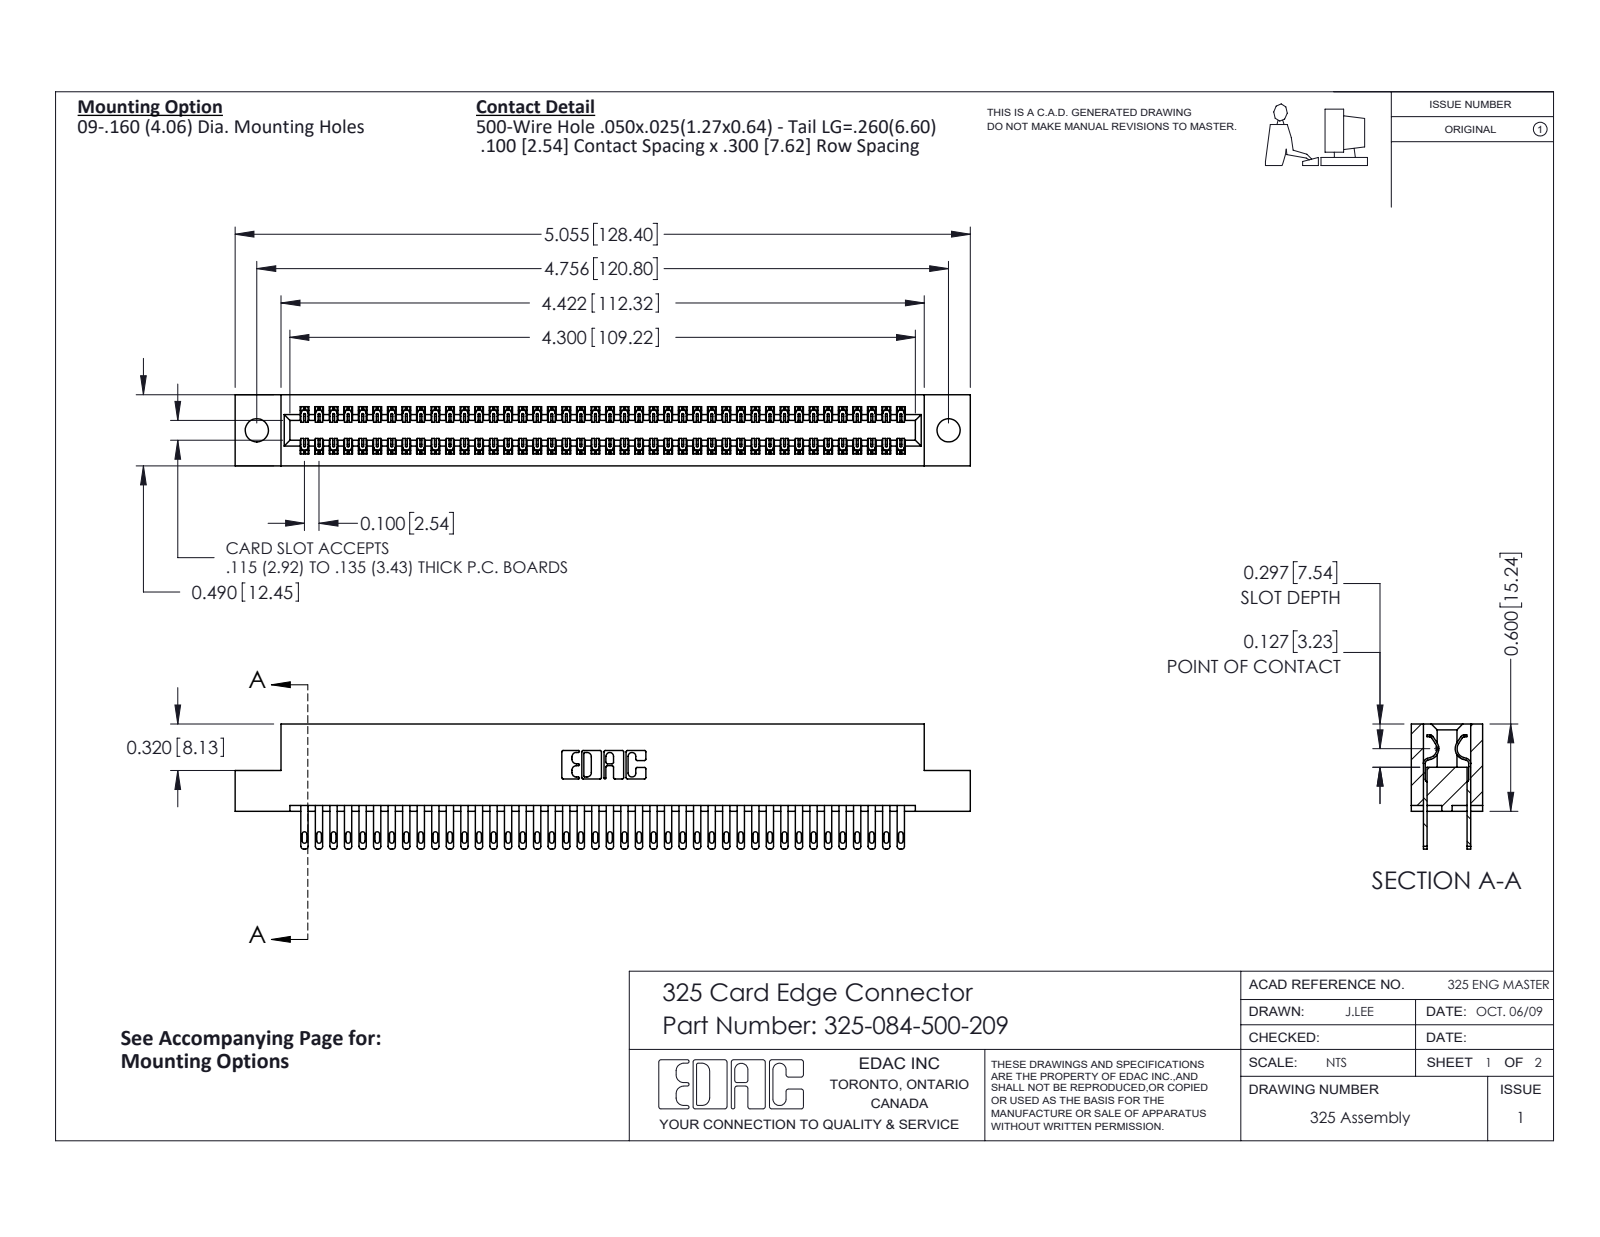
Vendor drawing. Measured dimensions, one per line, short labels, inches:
name: 325-292-001_325-293-100; 325-084-500-209; 325 Part_.160 TH
written by: SolidWorks 2016 (CONFIG_CONTROL_DESIGN)
unit: in
bodies: 85 solids, 4146 faces (2590 planar, 1556 cylindrical, 0 other)
size: 5.055 × 0.86 × 0.49
volume: 1.013 in³; area: 32.38 in²
holes: 2× ⌀0.16
rounds: 126× R0.006, 84× R0.016, 84× R0.02, 22× R0.01, 6× R0.007, 6× R0.031, 3× R0.026, 2× R0.014
face distances: 0.083, 0.407, 0.3, 0.107, 0.383, 0.025, 0.49, 0.325, 0.275, 0.56
hole spacings: 4.756
